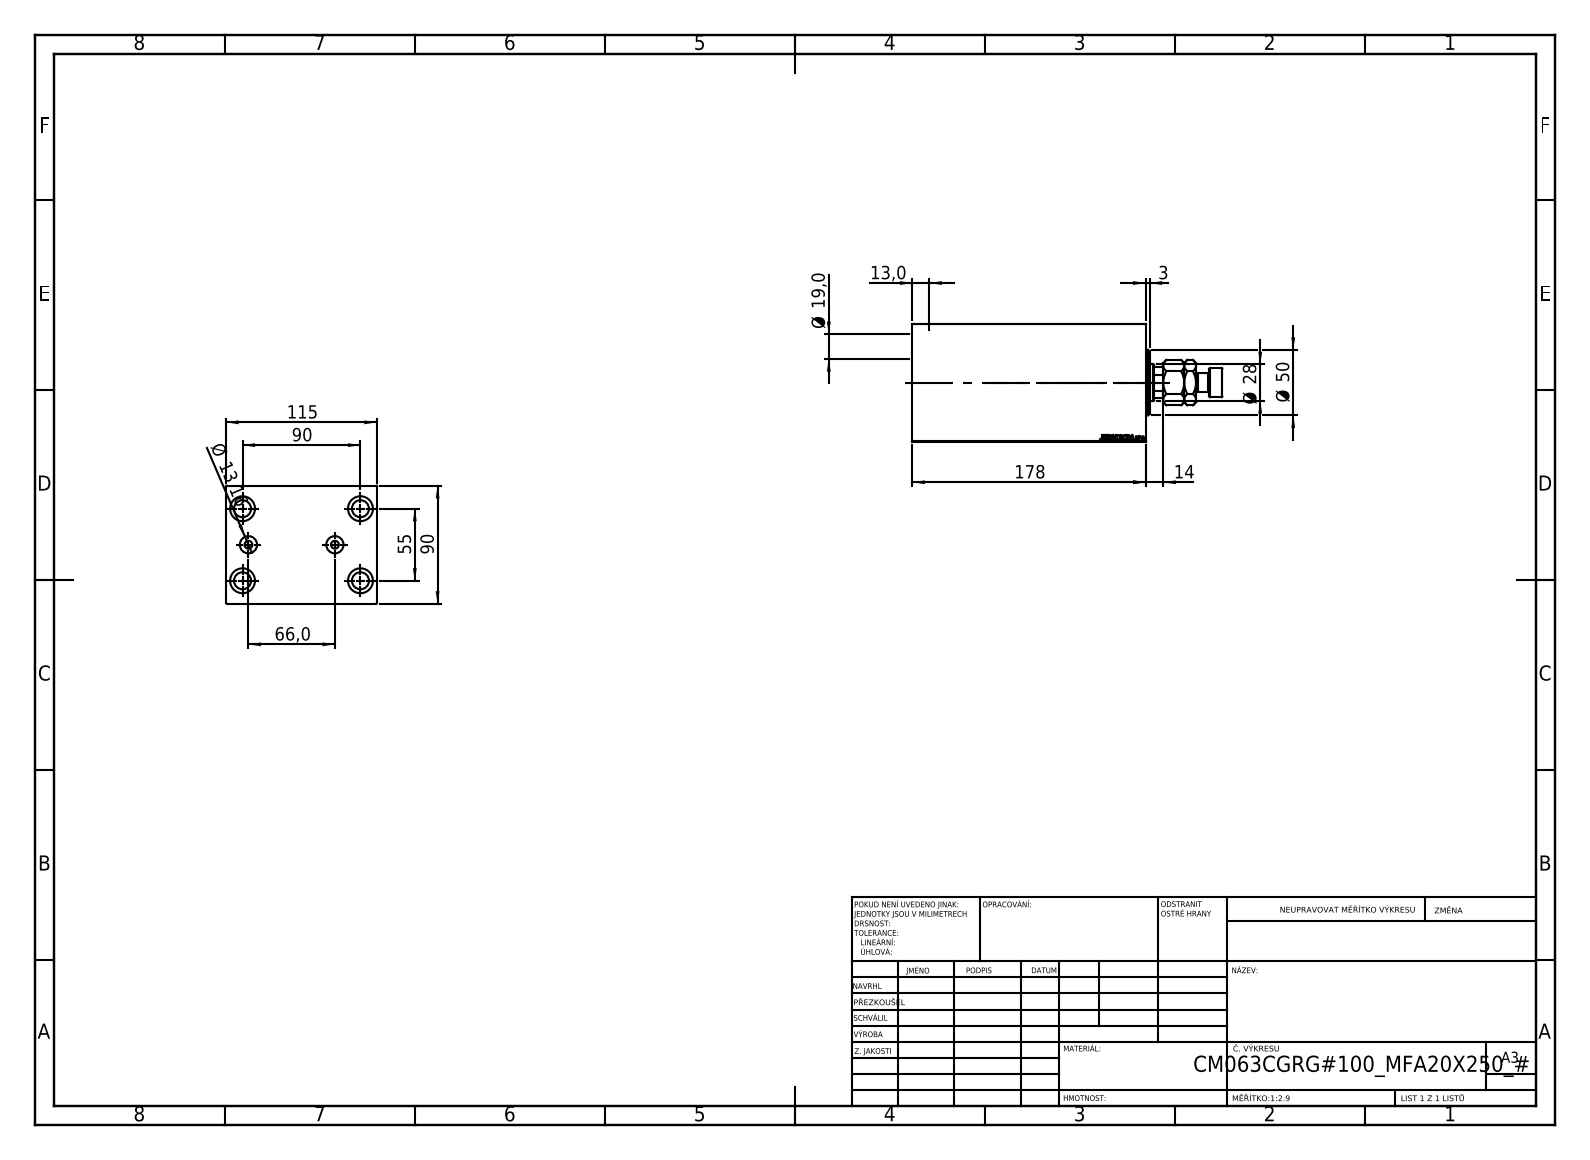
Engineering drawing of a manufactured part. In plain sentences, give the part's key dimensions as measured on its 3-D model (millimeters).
The part is named "V450CM_VC_B; V450CM_C_VCP; V450CM_C_Body; MFA". Its 3-D file was written by "SolidWorks 2019 (CONFIG_CONTROL_DESIGN)". It is 3 solids with 100 faces: 32 planar, 24 cylindrical and 44 other. Overall it measures 219 by 72 by 72 millimeters. Its volume is 285 430 cubic millimeters and its surface area 45 342 square millimeters. Round holes: 1 of diameter 18.5, 1 of diameter 28, 1 of diameter 31.5. Round bosses or shafts: 1 of diameter 72, 1 of diameter 65, 1 of diameter 63, 1 of diameter 50, 1 of diameter 22, 1 of diameter 14. Partial cylindrical surfaces (rounded edges, fillets, slot ends): 1 of radius 13.5. The main face-to-face distances are 13.5, 147, 47, 100, 113.5, 160.5, 3, 30, 27, 16.5.
